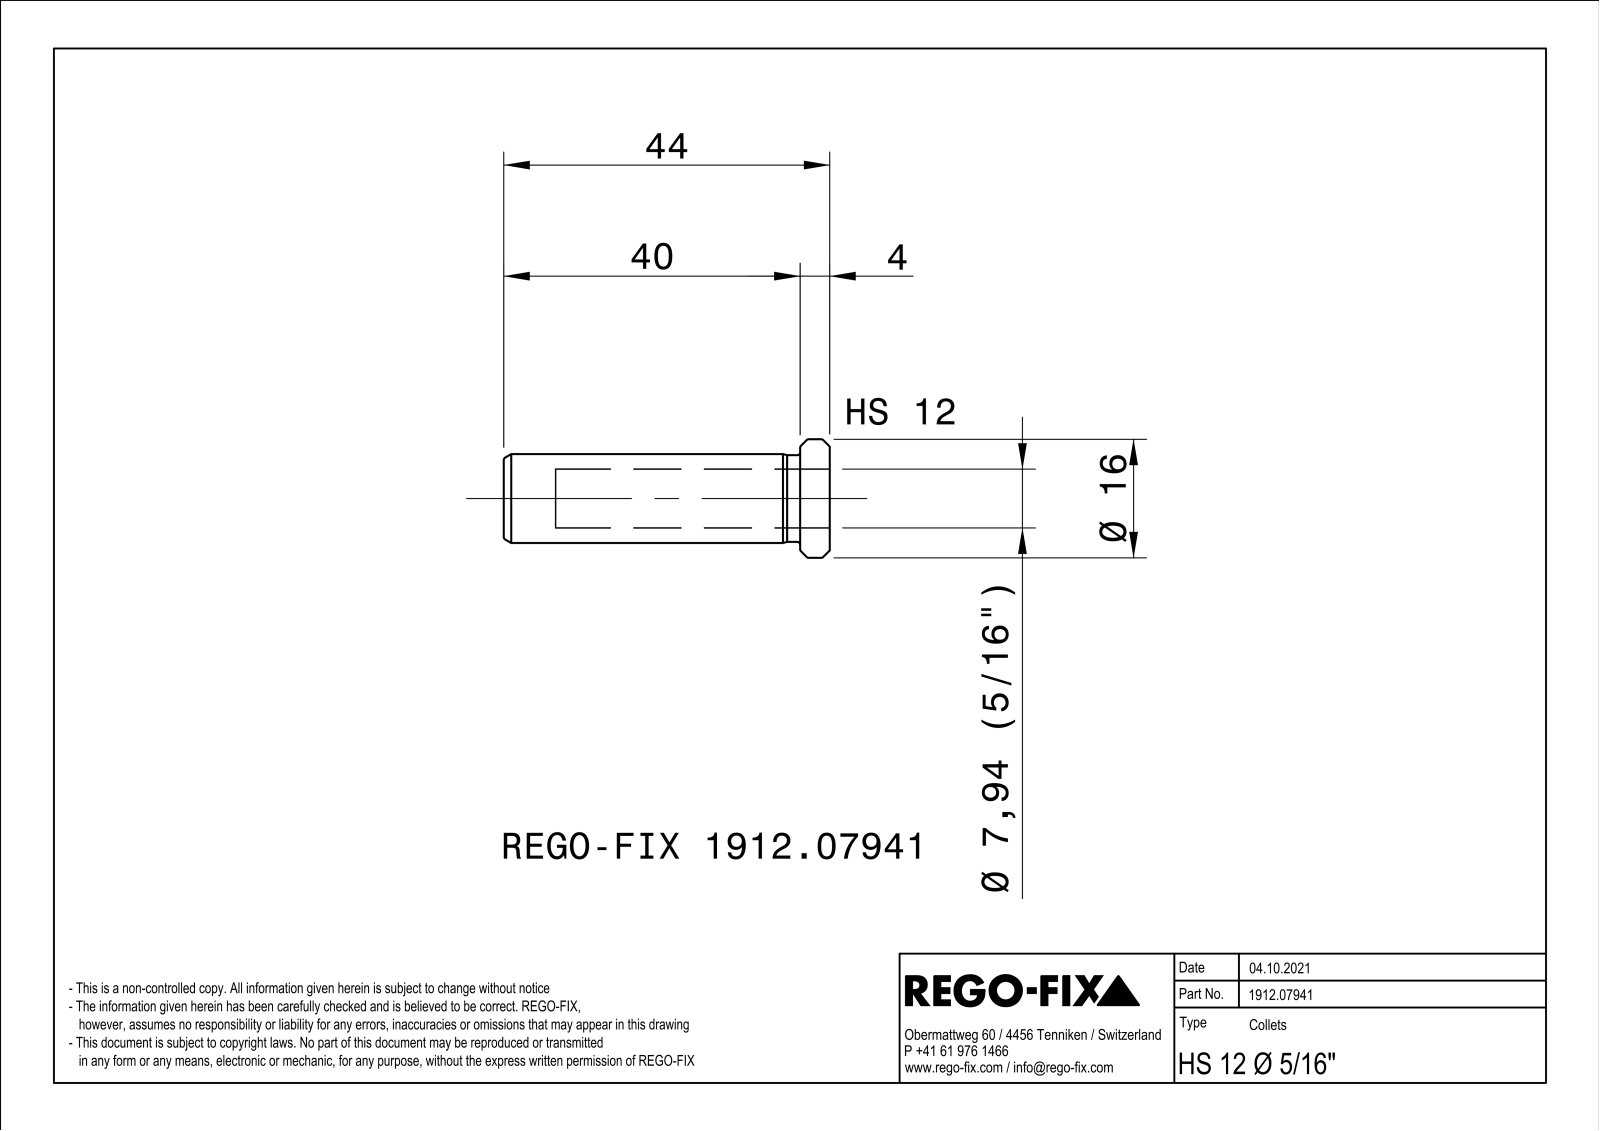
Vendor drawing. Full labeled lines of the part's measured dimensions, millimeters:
Part name (STEP PRODUCT): NOCUT
STEP written by: SIEMENS PLM Software Solid Edge ST10 (AUTOMOTIVE_DESIGN)
Units: millimetres
Bodies: 1 solid, 69 faces (22 planar, 11 cylindrical, 36 other)
Overall size (bounding box): 44 × 15.98 × 15.98
Volume: 2 831 mm³ · Surface area: 3 413 mm²
Round holes (diameter × count): ⌀7.94 ×1, ⌀8.2 ×1
Round bosses / shafts (diameter × count): ⌀16 ×1, ⌀12 ×1, ⌀11.7 ×1
Main face-to-face distances: 0.8, 44, 4, 40
